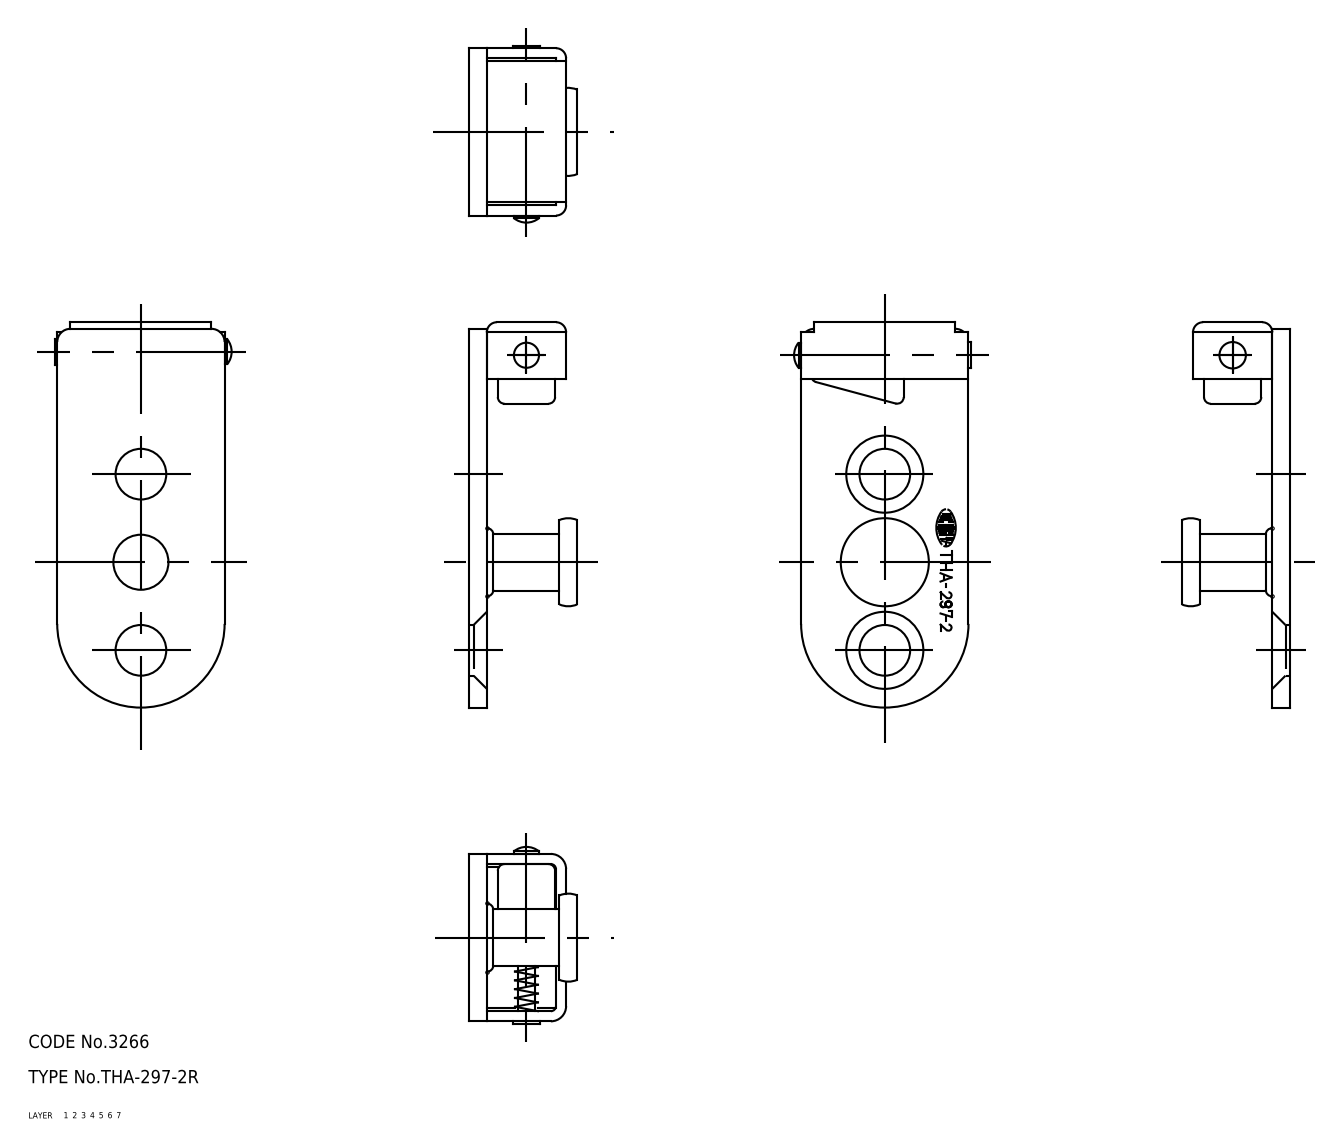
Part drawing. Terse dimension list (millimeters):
name: spring_mr; slider_mr; pin_B_mr; pin_A_mr (+3 more)
written by: CADfix (AUTOMOTIVE_DESIGN)
unit: mm
bodies: 6 solids, 110 faces (0 planar, 0 cylindrical, 110 other)
size: 87.5 × 40.1 × 24.5
volume: 21 962 mm³; area: 14 960 mm²
